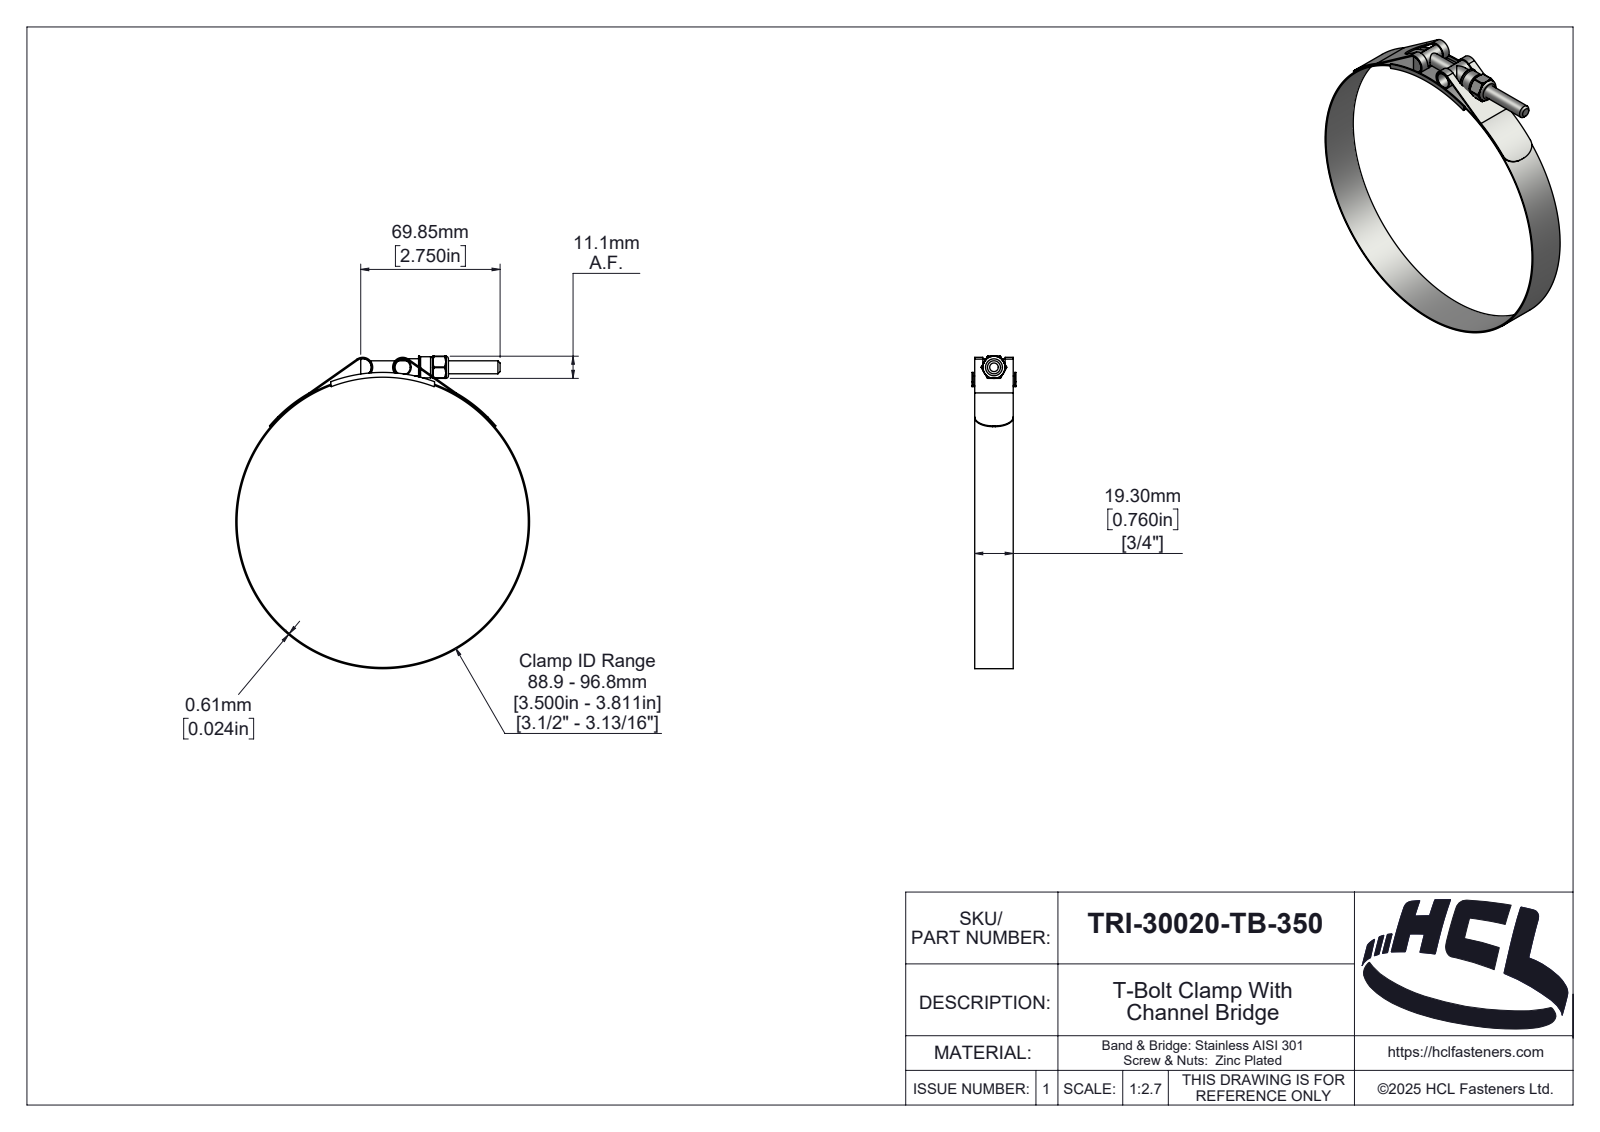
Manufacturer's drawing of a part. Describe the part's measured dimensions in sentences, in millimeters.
The part is named "TRI-30020-TB-350". Its 3-D file was written by "SolidWorks 2025 (AUTOMOTIVE_DESIGN)". It is 6 solids with 330 faces: 44 planar, 122 cylindrical and 164 other. Overall it measures 156.69 by 147.22 by 22 millimeters. Its volume is 11 512 cubic millimeters and its surface area 29 273 square millimeters. Round holes: 1 of diameter 5.4, 1 of diameter 6.35, 1 of diameter 6.5, 1 of diameter 7.58, 1 of diameter 146. Round bosses or shafts: 2 of diameter 8.58, 1 of diameter 147.22, 1 of diameter 10.58. Partial cylindrical surfaces (rounded edges, fillets, slot ends): 6 of radius 0.39, 2 of radius 0.5, 2 of radius 4.39, 2 of radius 5, 1 of radius 0.59, 1 of radius 2.42, 1 of radius 3.03, 1 of radius 3.19. The main face-to-face distances are 0.61, 19.3, 1.35, 20.65, 0.74, 21.39, 20.04, 22, 11.11, 20.78. The hole center spacings are 78.
